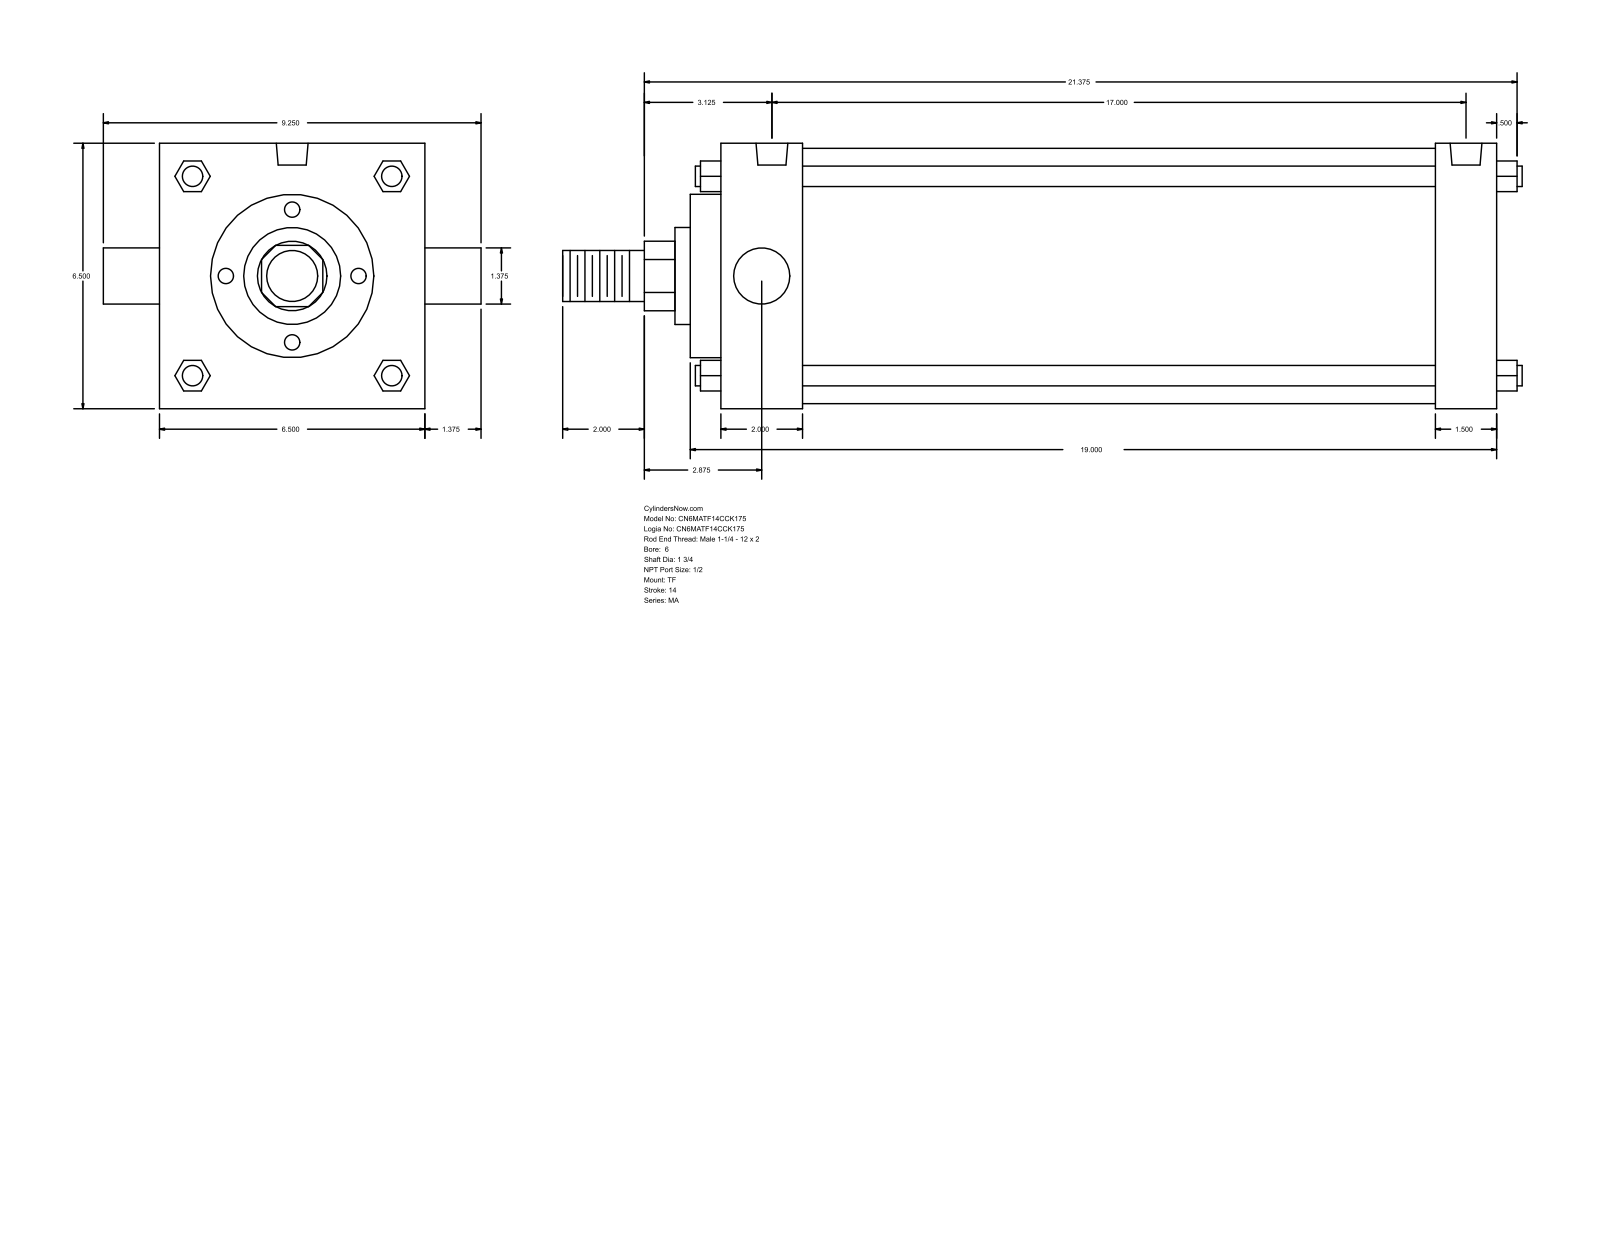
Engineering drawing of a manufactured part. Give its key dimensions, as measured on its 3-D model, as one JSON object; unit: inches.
{"part_name": "MA_TF__0600_1.75", "step_written_by": "GSSL Pune (CONFIG_CONTROL_DESIGN)", "units": "inches", "bodies": {"solids": 0, "faces": 122, "planar": 93, "cylindrical": 29, "other": 0}, "overall_size": [23.5, 9.25, 6.5], "round_holes": [[0.687, 3], [0.778, 2]], "round_bosses_or_shafts": [[0.5, 4], [6.25, 1], [4, 1], [2.375, 1], [1.75, 1], [1.375, 1], [1.25, 1]], "partial_cylinders_radius": [[0.852, 1]], "face_to_face_distances": [6.5, 19, 0.75, 2, 17.5, 17, 15.5, 1.5, 2.75, 18.25], "hole_center_spacings": [17]}
